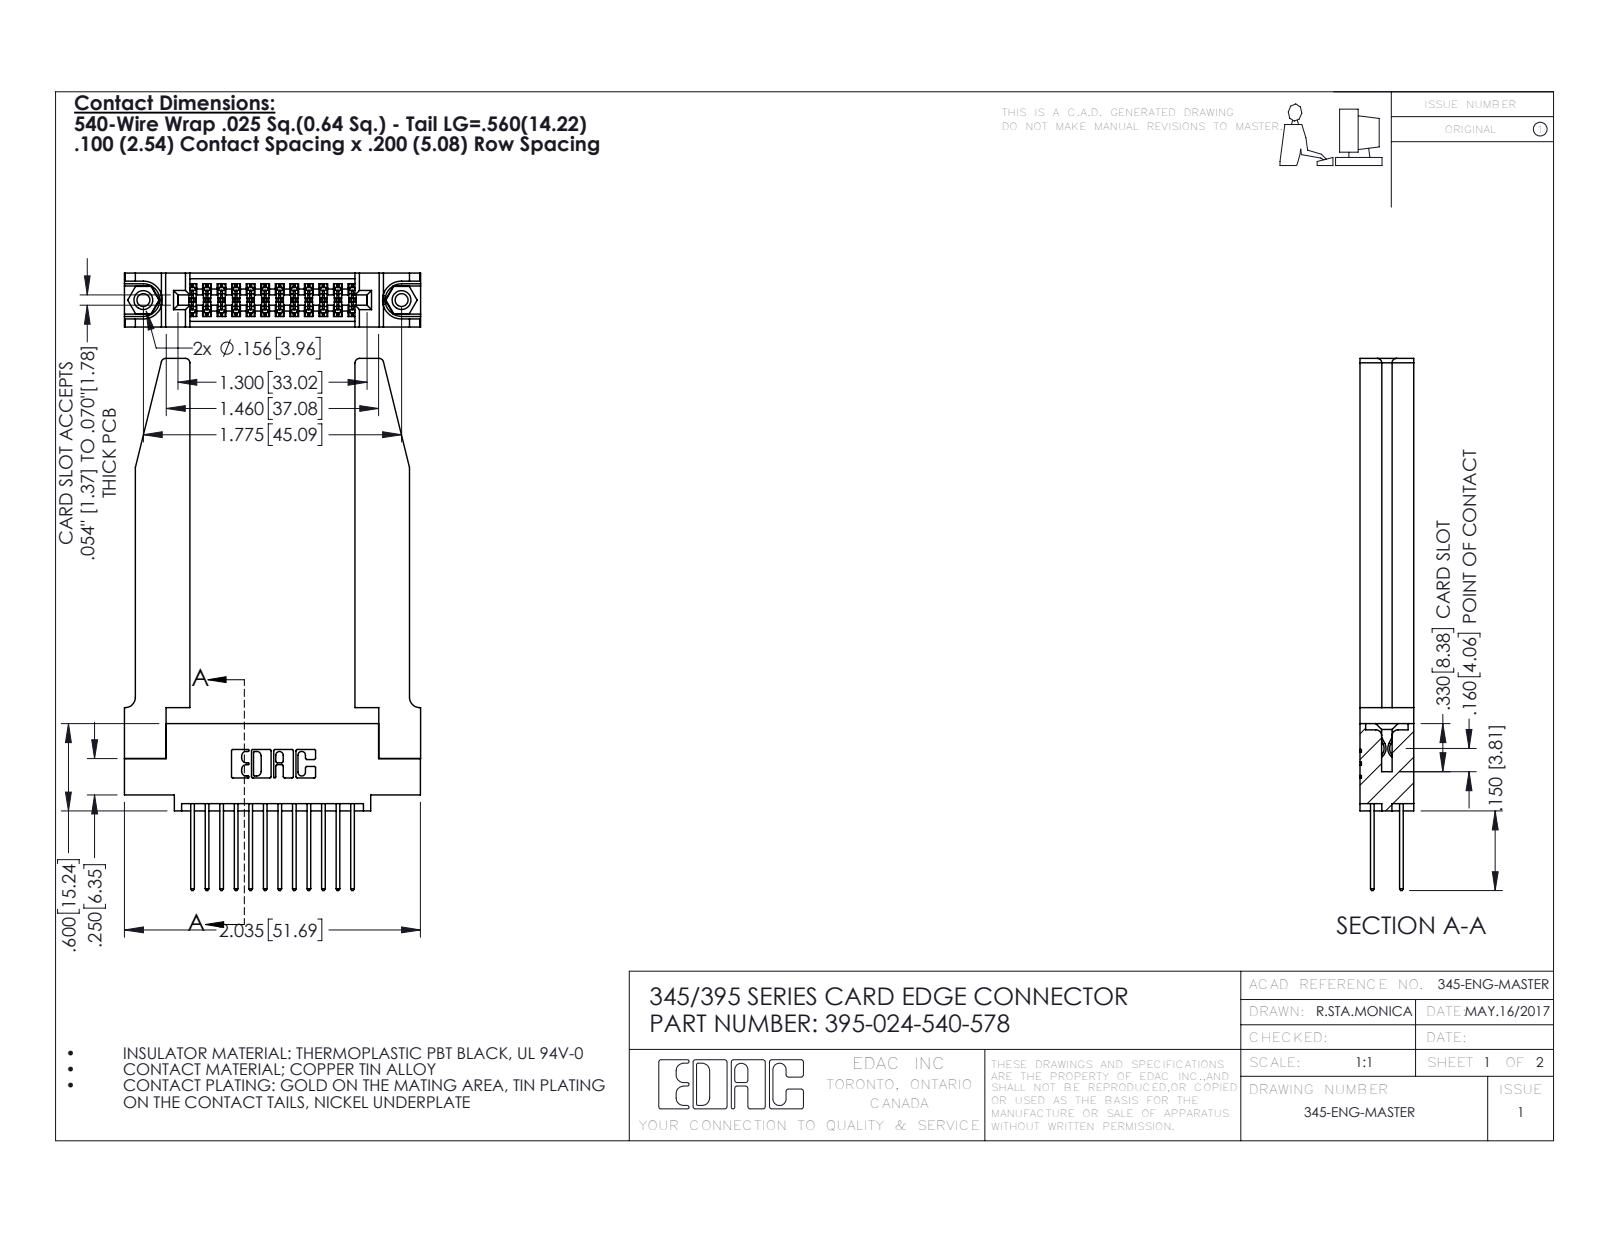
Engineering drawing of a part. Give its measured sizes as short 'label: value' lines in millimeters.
name: 395-024-540-578; 345-250-001_345-250-001-102; 345-220-078_345-220-078; 345-292-001_345-293-140 (+1 more)
written by: SolidWorks 2016 (CONFIG_CONTROL_DESIGN)
unit: mm
bodies: 29 solids, 1564 faces (1018 planar, 494 cylindrical, 52 other)
size: 92.9 × 51.7 × 9.4
volume: 12 500 mm³; area: 13 810 mm²
holes: 2× ⌀2.3, 2× ⌀3.2, 2× ⌀4, 1× ⌀1.6
bosses: 2× ⌀3.9
rounds: 36× R0.2, 24× R0.3, 22× R0.3, 8× R0.8, 6× R0.2, 6× R0.8, 3× R0.7, 2× R0.4
face distances: 9.4, 1.8, 7.6, 5.1, 2.5, 6.9, 0.6, 3.8, 3.8, 5.6
hole spacings: 6.9, 39.2, 45.1
